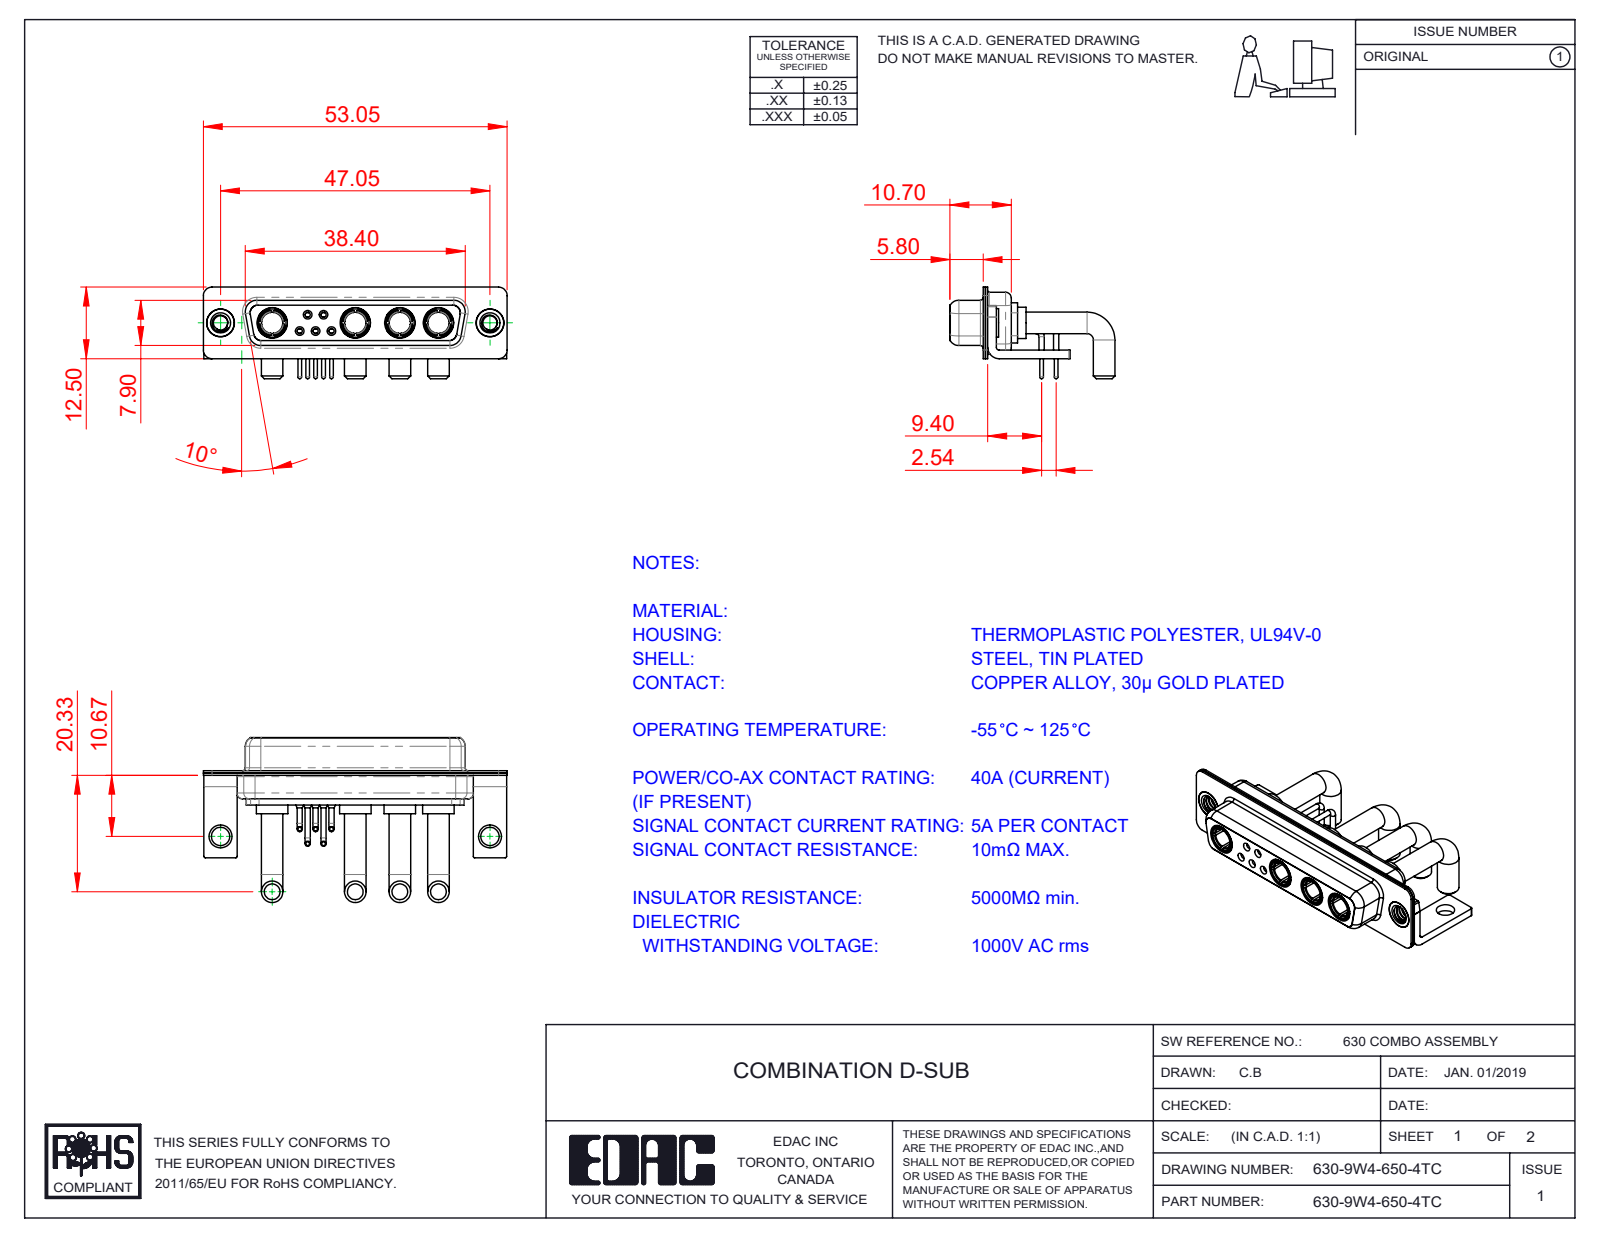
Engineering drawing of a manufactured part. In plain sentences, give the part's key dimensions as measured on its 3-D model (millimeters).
The part is named "630Combo Shell Front_25 Contacts; 630Combo Shell Rear_25 Contacts; 630-9W4-650-4TC; 630Combo Threaded Rivet_B (+5 more)". Its 3-D file was written by "SolidWorks 2020 (CONFIG_CONTROL_DESIGN)". It is 20 solids with 894 faces: 278 planar, 370 cylindrical and 246 other. Overall it measures 53.05 by 28.8 by 16 millimeters. Its volume is 4 891 cubic millimeters and its surface area 9 944 square millimeters. Round holes: 6 of diameter 4.85, 5 of diameter 0.9, 5 of diameter 1.1, 5 of diameter 1.5, 5 of diameter 2, 4 of diameter 3.7, 4 of diameter 5.3, 3 of diameter 1.6, 2 of diameter 1.7, 2 of diameter 2.5, 2 of diameter 3.2, 2 of diameter 4. Round bosses or shafts: 8 of diameter 3.75, 5 of diameter 0.9, 5 of diameter 0.65, 4 of diameter 5.5, 4 of diameter 5.2, 4 of diameter 4.96, 4 of diameter 4.75, 2 of diameter 5. Partial cylindrical surfaces (rounded edges, fillets, slot ends): 16 of radius 0.25, 16 of radius 1.5, 13 of radius 2, 8 of radius 1.35, 8 of radius 1.6, 5 of radius 0.5, 4 of radius 0.6, 4 of radius 0.65. The main face-to-face distances are 0.4, 0.45, 1.4, 8.45, 1.8, 0.8, 8.9, 6.2, 1.5, 7.05. The hole center spacings are 3.16, 2.77, 47.05, 4.4, 5.02, 5.03, 5.04, 5.54.
